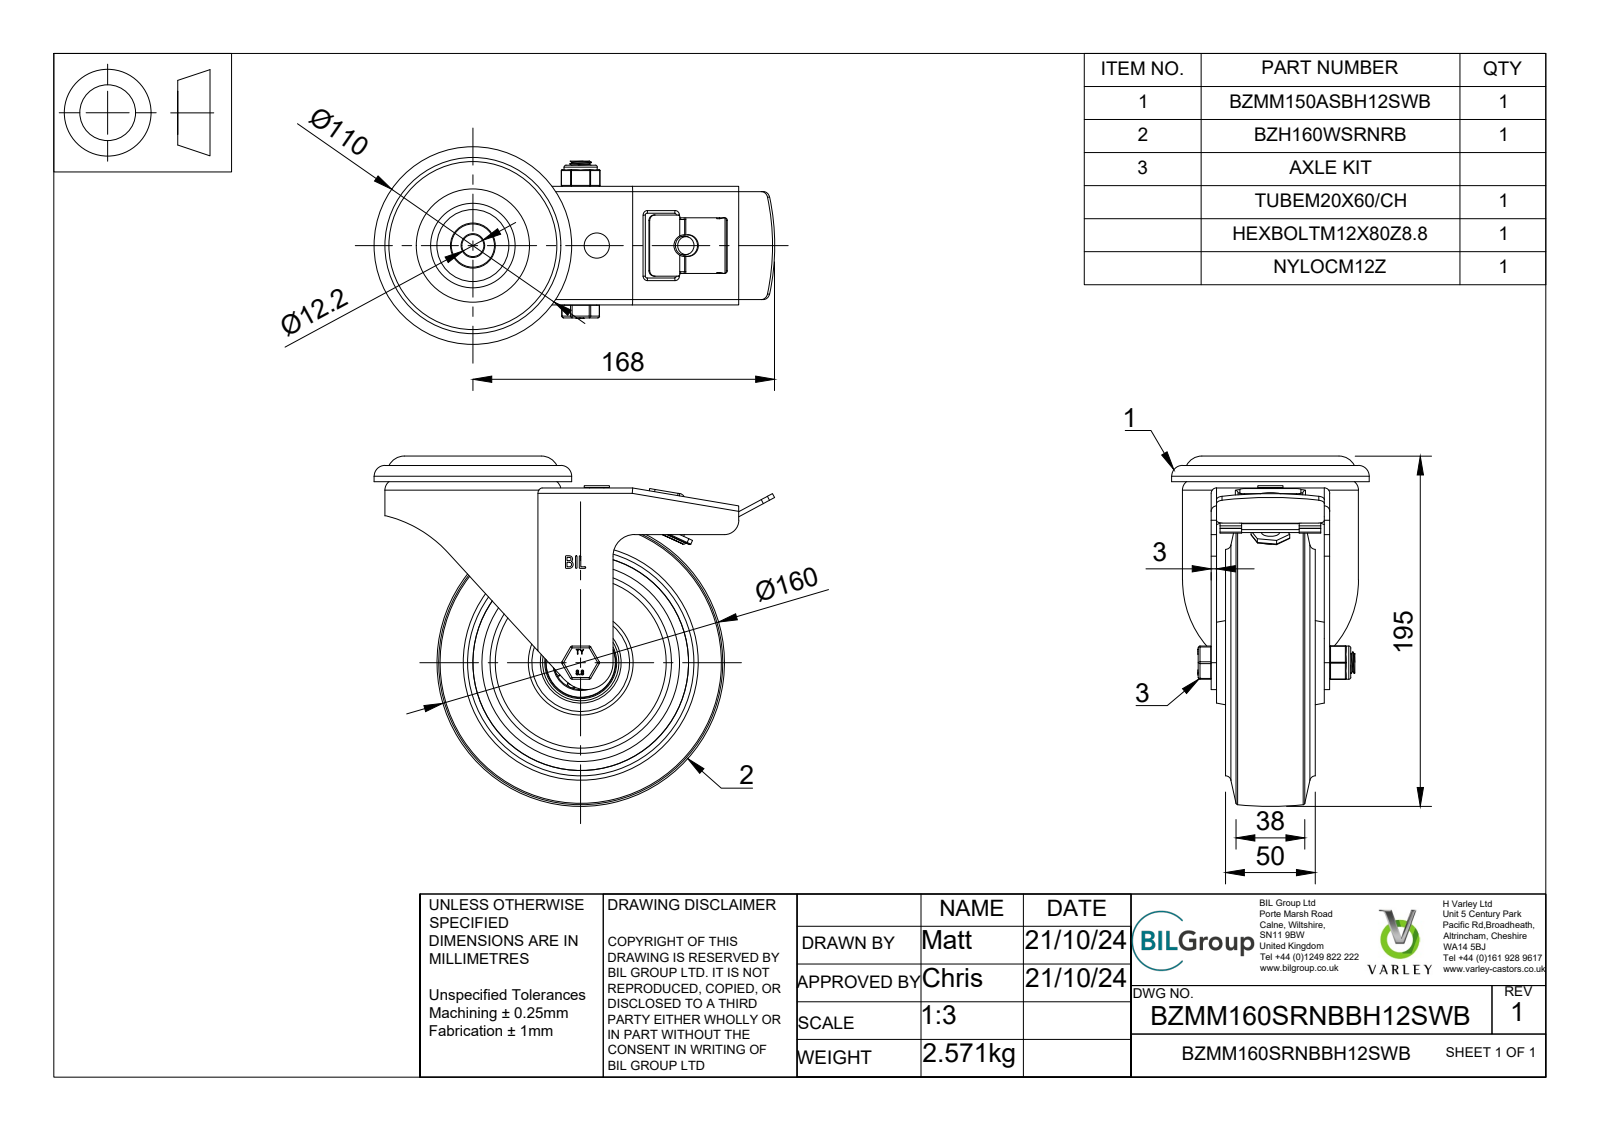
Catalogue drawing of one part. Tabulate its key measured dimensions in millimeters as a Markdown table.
| quantity | value |
| --- | --- |
| part name | BZMM160SRNBBH12SWB v3; BZMM150ASBH12SWB v1; ZINC PLATED, PRESSED STEEL TOP PLATE; ZINC PLATED, PRESSED STEEL FORKS (+8 more) |
| STEP written by | Autodesk Translation Framework v13.20.0.188 (AUTOMOTIVE_DESIGN) |
| units | millimeters |
| bodies | 22 solids, 668 faces (338 planar, 195 cylindrical, 135 other) |
| overall size | 223 × 195 × 110 |
| volume | 829 431 mm³ |
| surface area | 278 421 mm² |
| round holes (diameter × count) | 8 × 2, 12 × 1, 12.1 × 1, 12.2 × 1, 12.5 × 1, 14 × 1, 20 × 1, 30 × 1, 33.5 × 1, 34 × 1, 40 × 1, 52.5 × 1 |
| round bosses / shafts (diameter × count) | 5 × 8, 110 × 1, 77 × 1, 40 × 1, 25 × 1, 24.5 × 1, 19.9 × 1, 18.5 × 1 |
| partial cylindrical surfaces (radius × count) | 0.5 × 24, 1 × 18, 1.5 × 12, 3 × 8, 2 × 3, 2.5 × 3, 4 × 2, 6 × 2 |
| main face-to-face distances | 3, 63, 8, 1.5, 30, 36, 27, 33, 5, 4.75 |
| hole center spacings | 69 |
